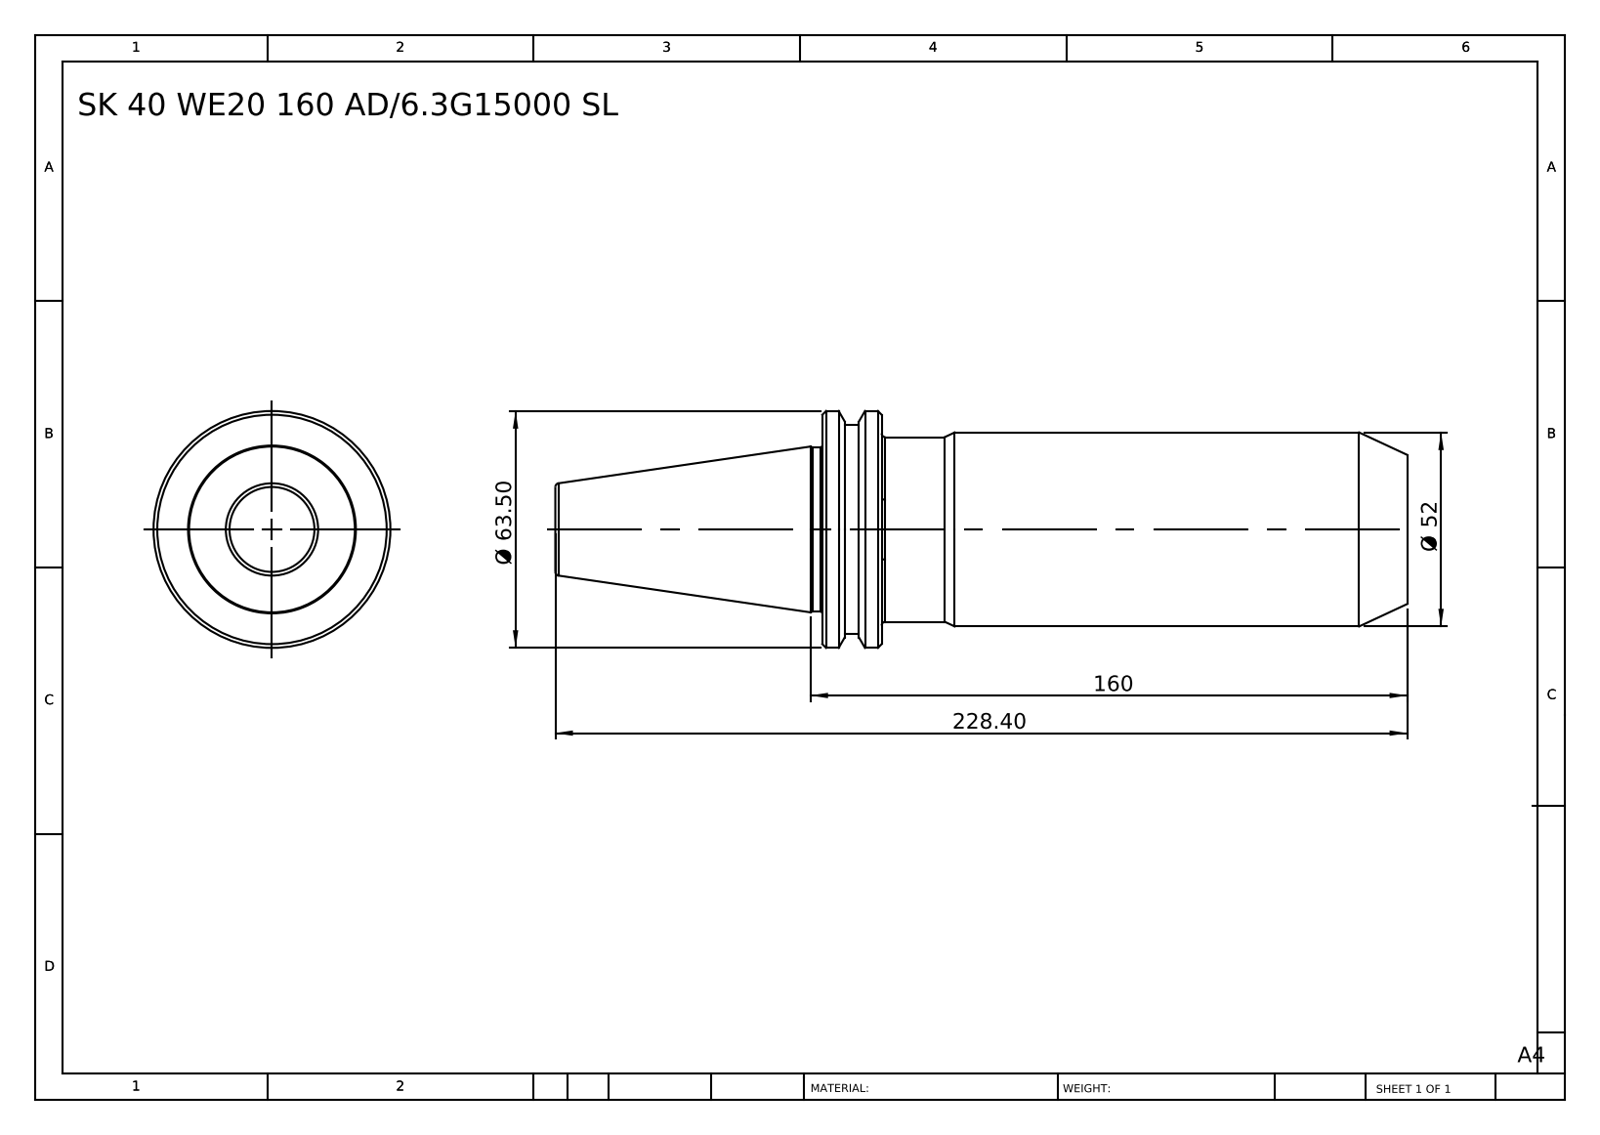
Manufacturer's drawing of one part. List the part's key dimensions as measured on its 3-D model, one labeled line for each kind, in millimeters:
Part name (STEP PRODUCT): SK40 WE20 160 AD-6.3G15000 SL
STEP written by: SolidWorks 2014 (CONFIG_CONTROL_DESIGN)
Units: millimetres
Bodies: 1 solid, 40 faces (6 planar, 12 cylindrical, 22 other)
Overall size (bounding box): 228.4 × 63.5 × 63.5
Volume: 406 913 mm³ · Surface area: 39 076 mm²
Round bosses / shafts (diameter × count): ⌀63.5 ×1, ⌀56 ×1, ⌀52 ×1, ⌀49.5 ×1, ⌀44 ×1
Main face-to-face distances: 156.8, 140.9, 15.9, 228.4, 87.5, 71.6, 147, 6.1, 9.8, 81.4
